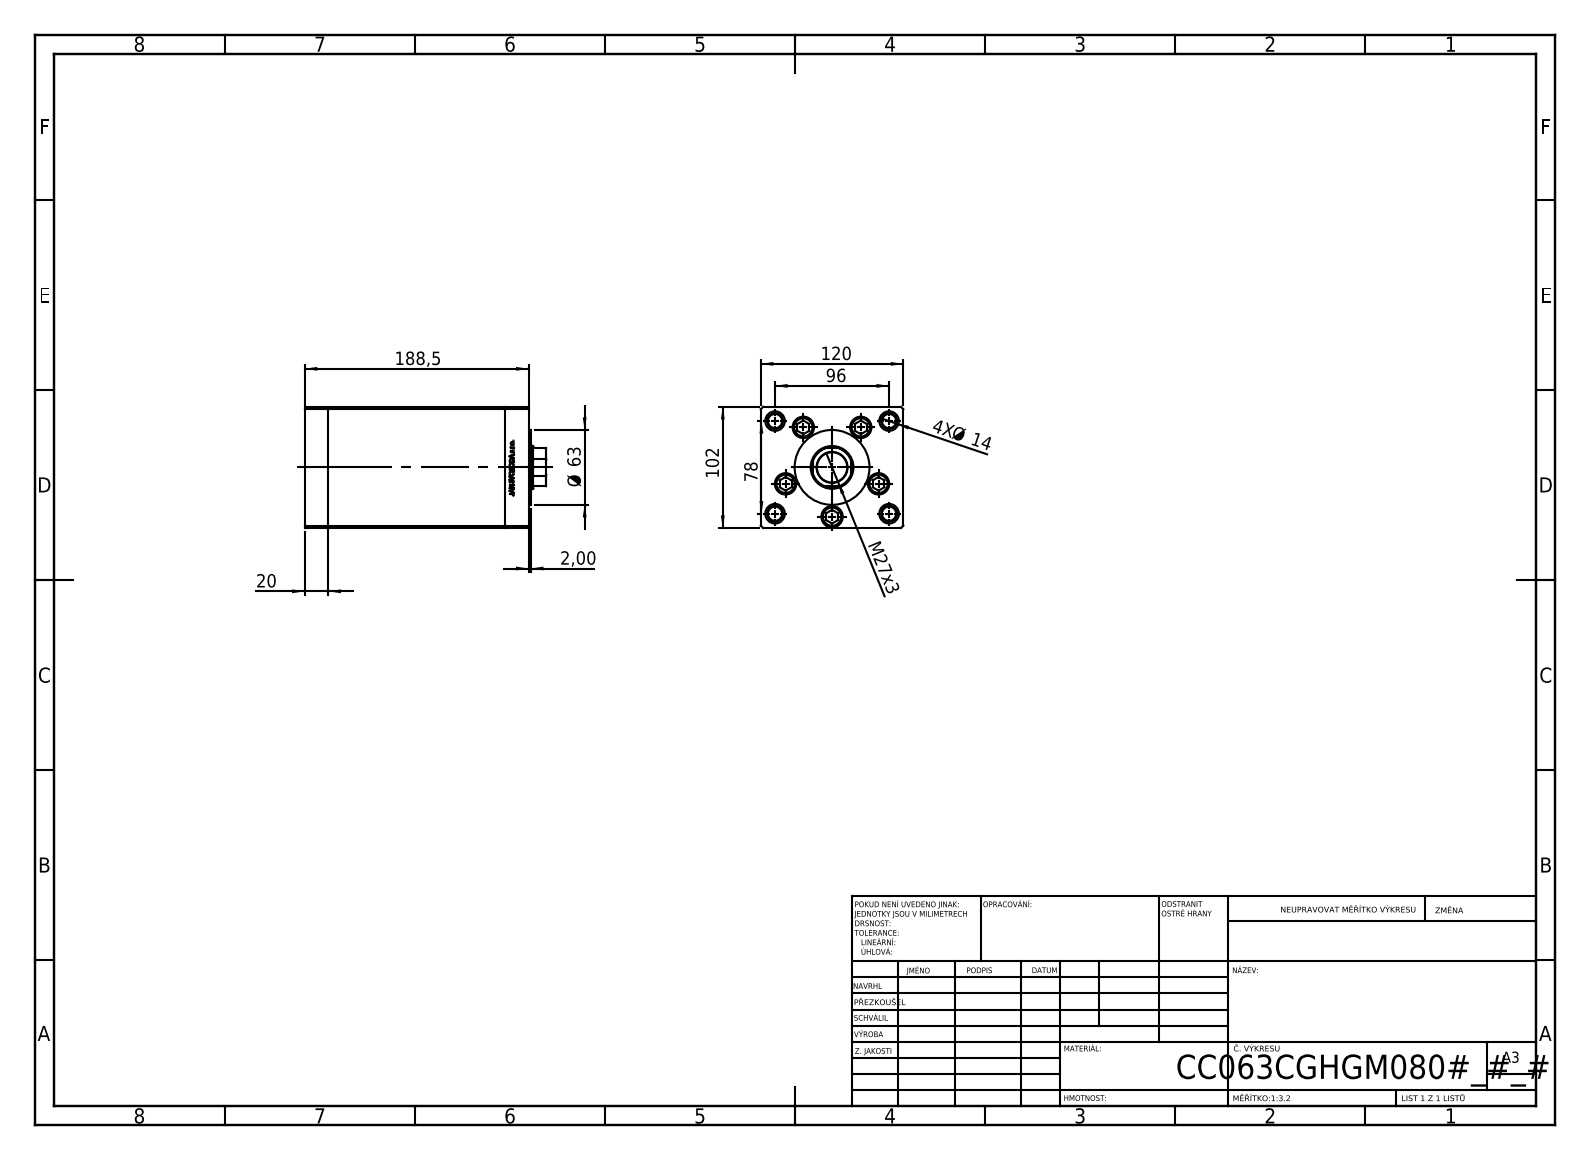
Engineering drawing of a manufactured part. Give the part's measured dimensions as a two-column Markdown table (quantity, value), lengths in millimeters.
| quantity | value |
| --- | --- |
| part name | V220C_C MIDDLE; V220C FRONT; V220C_VC_C; ALLEN BOLT (+1 more) |
| STEP written by | SolidWorks 2019 (CONFIG_CONTROL_DESIGN) |
| units | millimeters |
| bodies | 13 solids, 1185 faces (546 planar, 177 cylindrical, 462 other) |
| overall size | 203.5 × 120 × 102 |
| volume | 1 944 000 mm³ |
| surface area | 281 531 mm² |
| round holes (diameter × count) | 13.5 × 9, 18 × 5, 2 × 4, 12 × 4, 13.16 × 4, 16.5 × 4, 17 × 1, 25.5 × 1, 36 × 1 |
| round bosses / shafts (diameter × count) | 8 × 5, 17 × 4, 63 × 1 |
| partial cylindrical surfaces (radius × count) | 0.93 × 2, 17.5 × 1 |
| main face-to-face distances | 120, 20, 102, 148.5, 168.5, 34.25, 188.5, 154.25, 134.25, 14.25 |
| hole center spacings | 41.5, 61.85, 24.39, 26.69, 47.92, 48.07, 49.84, 53.57 |
